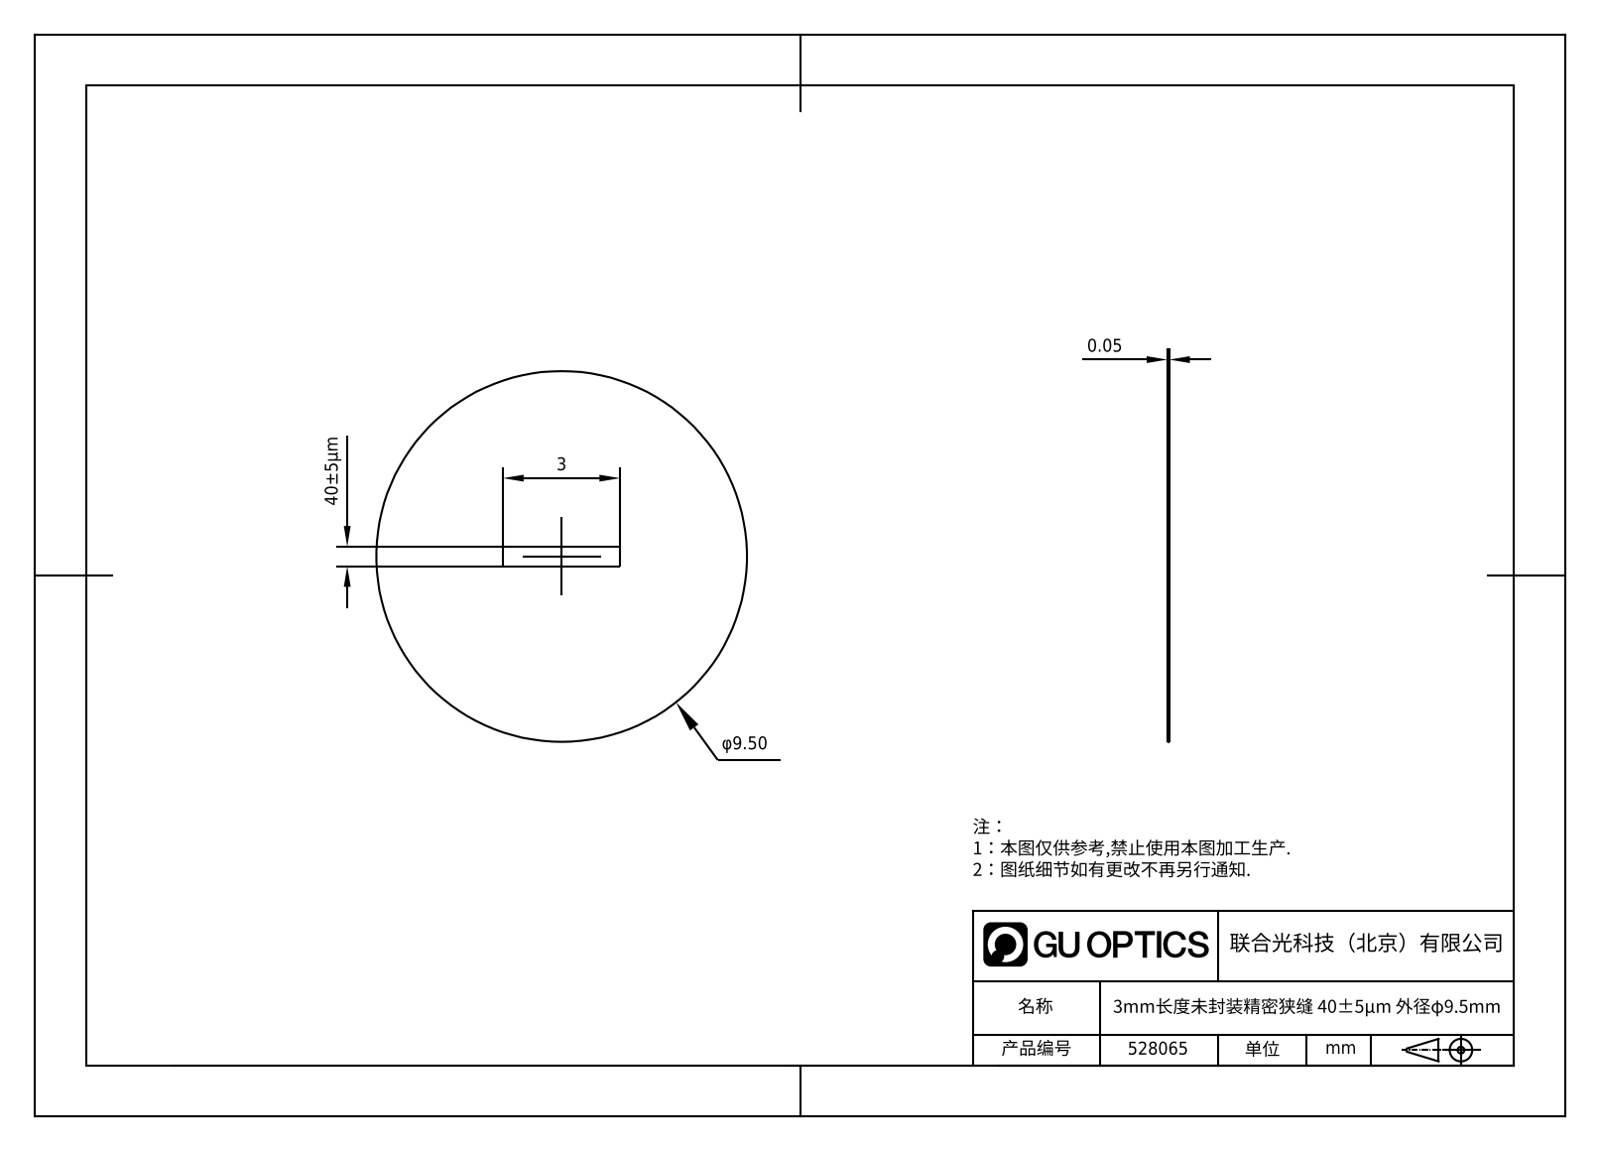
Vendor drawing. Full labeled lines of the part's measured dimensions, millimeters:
Part name (STEP PRODUCT): 1.5.4.6-ZXG-9.5-40
STEP written by: SolidWorks 2021 (CONFIG_CONTROL_DESIGN)
Units: millimetres
Bodies: 1 solid, 8 faces (6 planar, 2 cylindrical, 0 other)
Overall size (bounding box): 9.5 × 9.5 × 0.05
Volume: 4 mm³ · Surface area: 143 mm²
Round bosses / shafts (diameter × count): ⌀9.5 ×1
Main face-to-face distances: 3
